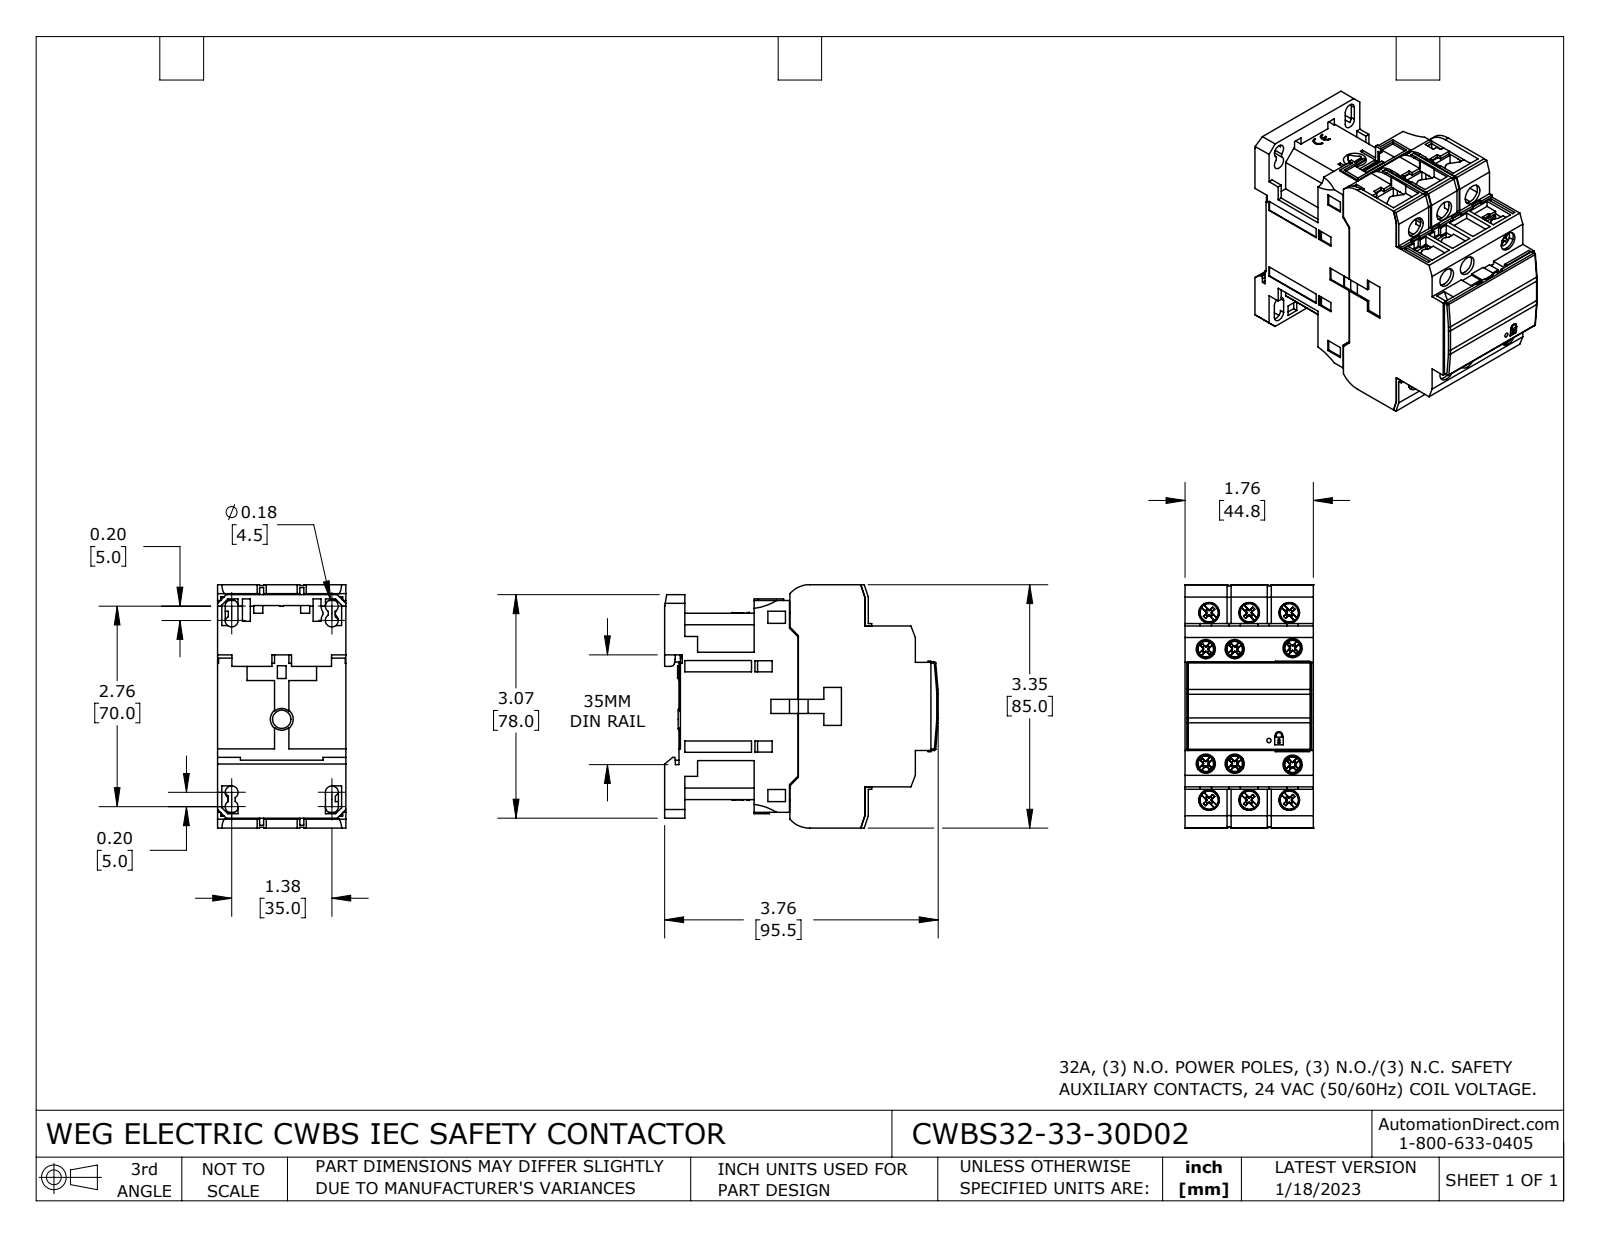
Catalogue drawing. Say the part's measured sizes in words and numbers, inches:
The part is named "CWBS32-33-30D02". Its 3-D file was written by "SolidWorks 2021 (CONFIG_CONTROL_DESIGN)". It is 42 solids with 2461 faces: 1808 planar, 446 cylindrical and 207 other. Overall it measures 3.76 by 3.346 by 1.764 inches. Its volume is 14.49 cubic inches and its surface area 108.8 square inches. Round holes: 6 of diameter 0.124, 6 of diameter 0.142, 6 of diameter 0.264, 6 of diameter 0.283, 4 of diameter 0.177, 1 of diameter 0.059. Round bosses or shafts: 6 of diameter 0.201, 6 of diameter 0.169, 6 of diameter 0.157, 6 of diameter 0.138, 4 of diameter 0.107, 2 of diameter 0.107. Partial cylindrical surfaces (rounded edges, fillets, slot ends): 42 of radius 0.02, 24 of radius 0.028, 12 of radius 0.071, 12 of radius 0.081, 12 of radius 0.964, 12 of radius 1.079, 12 of radius 2.128, 12 of radius 3.127. The main face-to-face distances are 1.764, 0.047, 1.691, 0.132, 1.823, 0.024, 0.217, 3.445, 0.276, 1.717. The hole center spacings are 0.551, 2.633, 2.575, 0.165, 0.174, 0.197, 0.398, 0.488.
